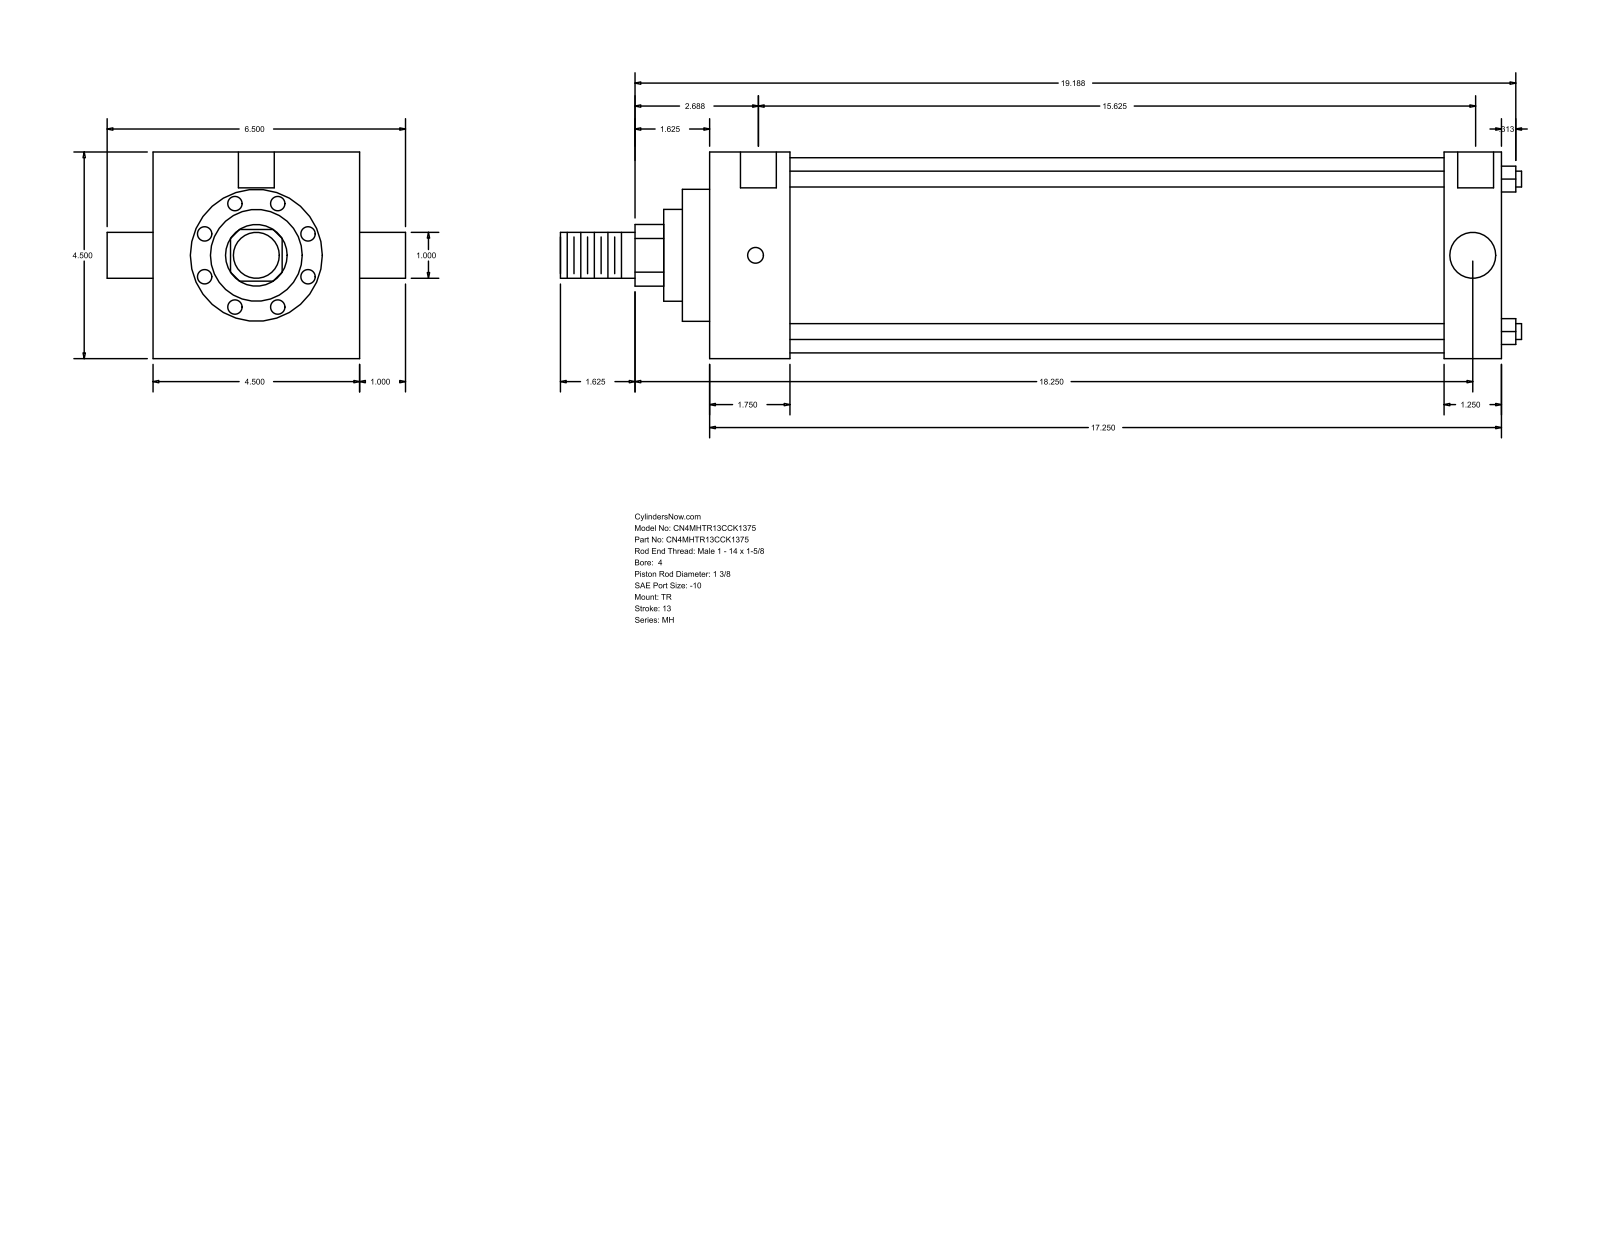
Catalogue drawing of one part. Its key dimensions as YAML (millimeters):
part_name: "MH_TR__0400_1.375"
step_written_by: "GSSL Pune (CONFIG_CONTROL_DESIGN)"
units: millimeters
bodies: {solids: 0, faces: 86, planar: 61, cylindrical: 25, other: 0}
overall_size: [531.81, 165.1, 114.3]
round_holes:
  - {diameter: 8.73, count: 3}
  - {diameter: 19.84, count: 2}
round_bosses_or_shafts:
  - {diameter: 8.76, count: 4}
  - {diameter: 25.4, count: 2}
  - {diameter: 107.95, count: 1}
  - {diameter: 73.03, count: 1}
  - {diameter: 50.8, count: 1}
  - {diameter: 34.92, count: 1}
partial_cylinders:
  - {radius: 17.06, count: 1}
face_to_face_distances: [114.3, 438.16, 44.45, 393.71, 406.41, 361.96, 31.75, 15.08, 59.53, 421.49]
hole_center_spacings: [1.59, 398.47, 396.88, 400.06]
